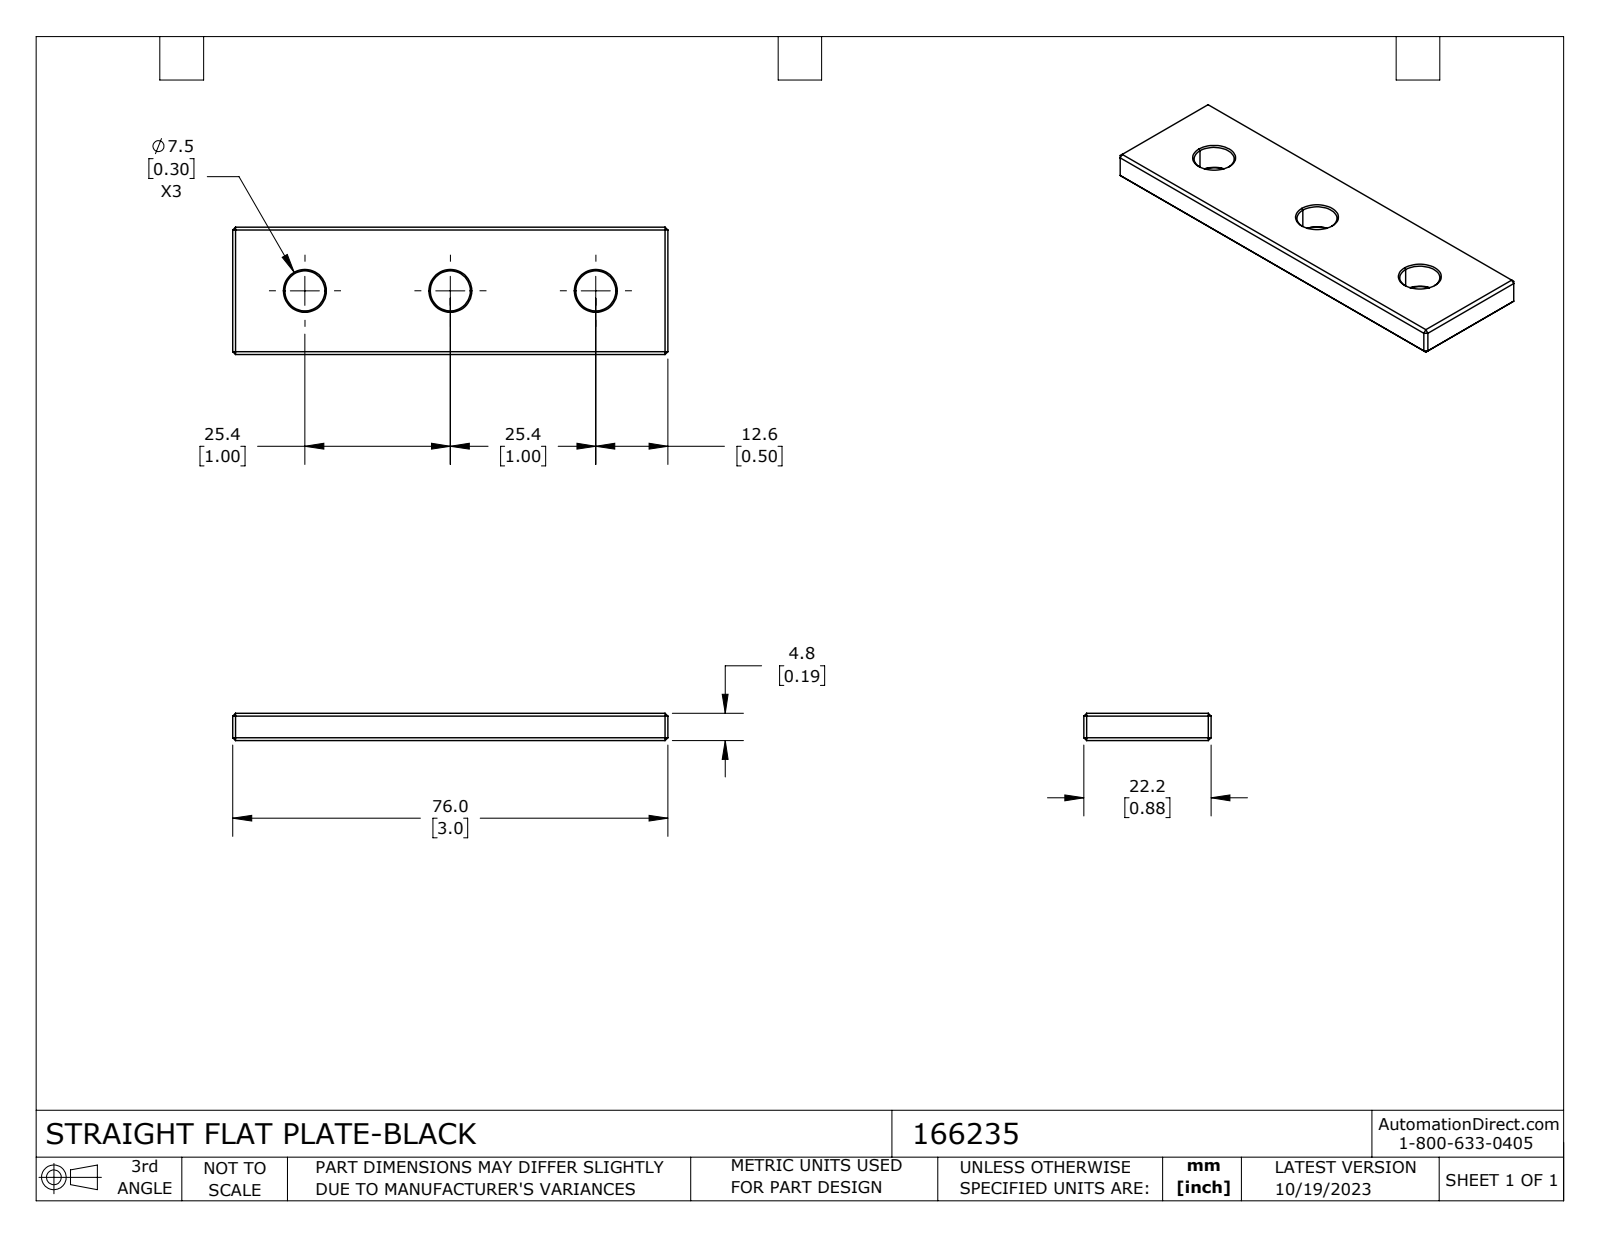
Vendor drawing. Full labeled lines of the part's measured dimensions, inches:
Part name (STEP PRODUCT): 166235
STEP written by: SolidWorks 2023 (CONFIG_CONTROL_DESIGN)
Units: inches
Bodies: 1 solid, 44 faces (26 planar, 6 cylindrical, 12 other)
Overall size (bounding box): 2.992 × 0.875 × 0.187
Volume: 0.454 in³ · Surface area: 6.598 in²
Round holes (diameter × count): ⌀0.276 ×3
Main face-to-face distances: 0.187, 0.875, 0.723, 2.992, 2.22, 2.706, 2.294
Hole centre spacings: 1, 2
